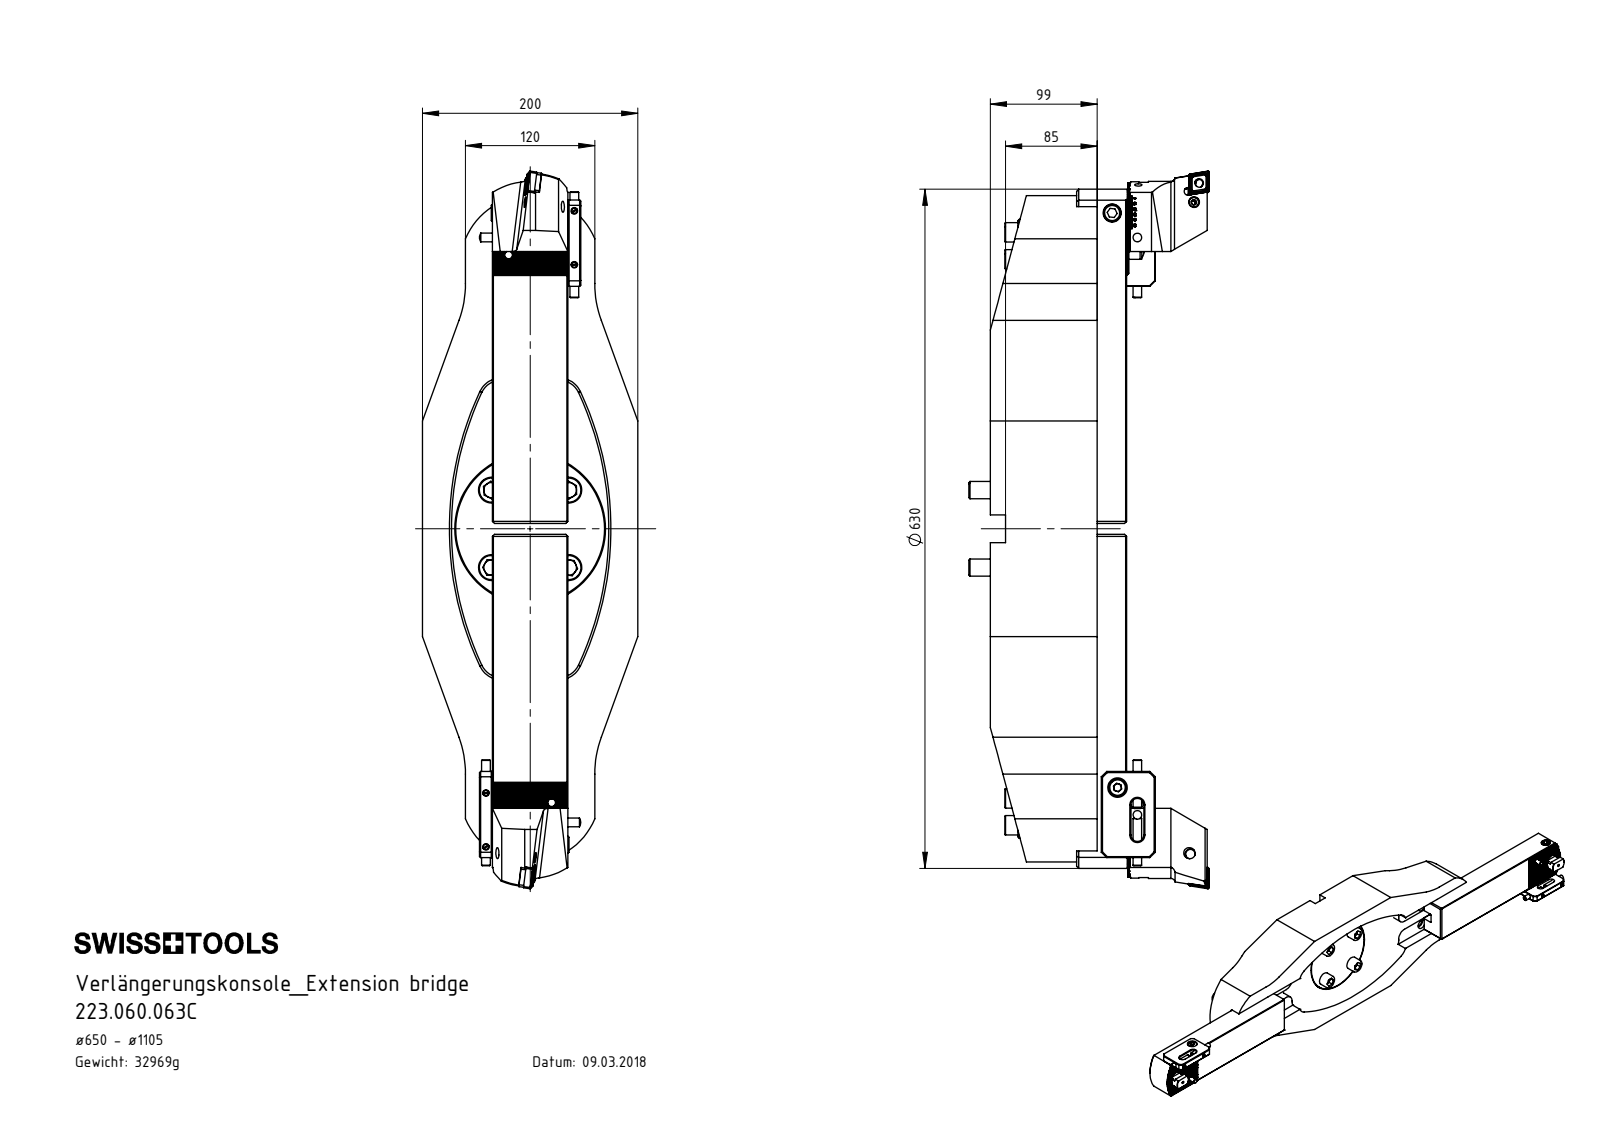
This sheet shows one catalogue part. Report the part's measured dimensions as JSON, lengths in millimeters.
{"part_name": "ISO 4028 - M8 x 35; ISO 8734 - 6 x 12; D60-VK3.063.080_B; CNMG190612 (+8 more)", "step_written_by": "SolidWorks 2017 (CONFIG_CONTROL_DESIGN)", "units": "millimeters", "bodies": {"solids": 86, "faces": 3665, "planar": 1810, "cylindrical": 950, "other": 905}, "overall_size": [665.59, 223.22, 200], "volume_mm3": 8596000, "surface_area_mm2": 943905, "round_holes": [[18, 40], [10.2, 34], [13, 16], [6.8, 6], [8, 6], [12, 6], [5, 4], [6, 4], [17, 4], [2, 2], [7.94, 2], [8.5, 2]], "round_bosses_or_shafts": [[24, 19], [12, 9], [16, 8], [10, 4], [6, 4], [18, 2], [9.9, 2], [8.6, 2]], "partial_cylinders_radius": [[0.14, 55], [2, 20], [1.2, 8], [1.8, 8], [4.15, 8], [22, 8], [15, 6], [65, 6]], "face_to_face_distances": [44, 20, 25, 60, 135, 65, 80, 99, 39, 19], "hole_center_spacings": [25, 47.17, 40, 50, 64.03, 475, 476.68, 150]}
